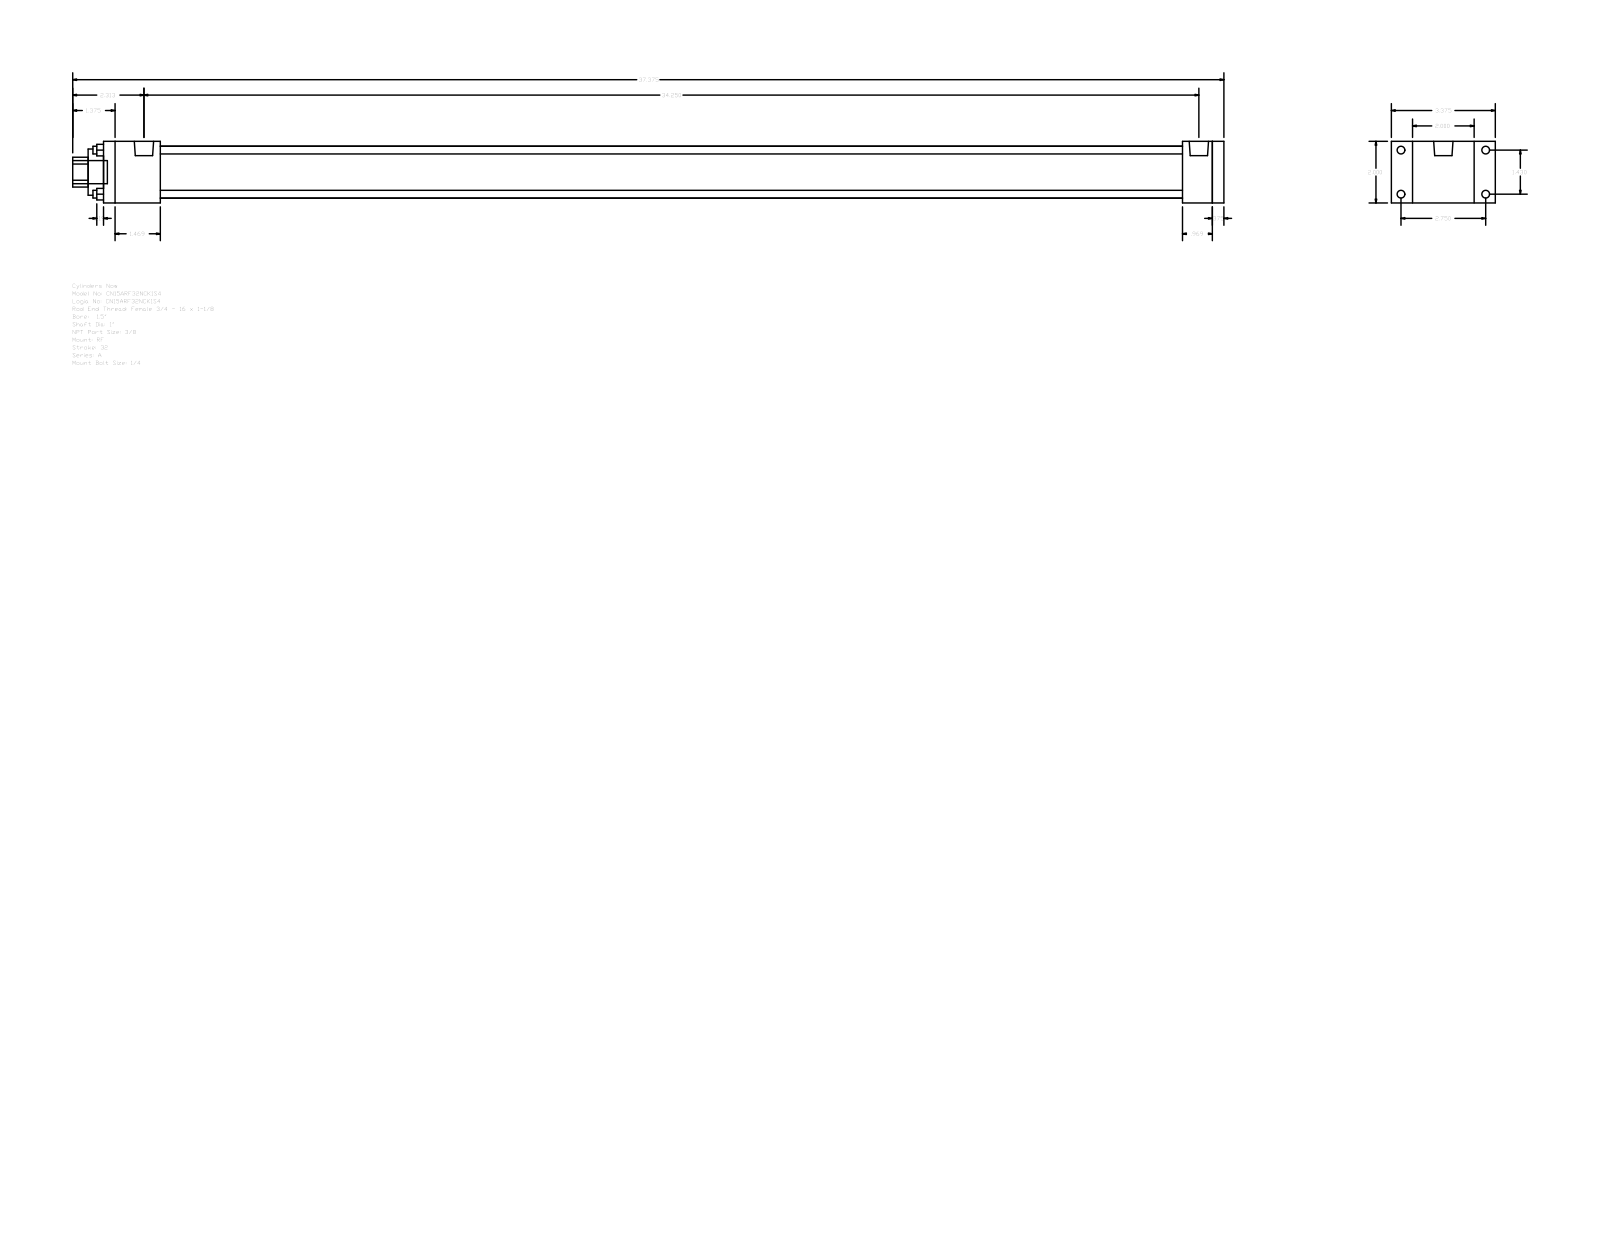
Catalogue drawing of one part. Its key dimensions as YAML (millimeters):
part_name: "A_RF__0150_1"
step_written_by: "GSSL Pune (CONFIG_CONTROL_DESIGN)"
units: millimeters
bodies: {solids: 0, faces: 92, planar: 64, cylindrical: 28, other: 0}
overall_size: [949.33, 85.72, 50.8]
round_holes:
  - {diameter: 6.35, count: 4}
  - {diameter: 25.4, count: 1}
  - {diameter: 38.1, count: 1}
  - {diameter: 42.93, count: 1}
round_bosses_or_shafts:
  - {diameter: 6.35, count: 4}
  - {diameter: 5.56, count: 4}
  - {diameter: 15.93, count: 2}
  - {diameter: 19.05, count: 1}
partial_cylinders:
  - {radius: 12.29, count: 1}
face_to_face_distances: [50.8, 9.53, 914.4, 923.93, 889.79, 24.61, 34.14, 46.83, 842.96, 867.57]
hole_center_spacings: [25.68, 36.32, 51.36]
